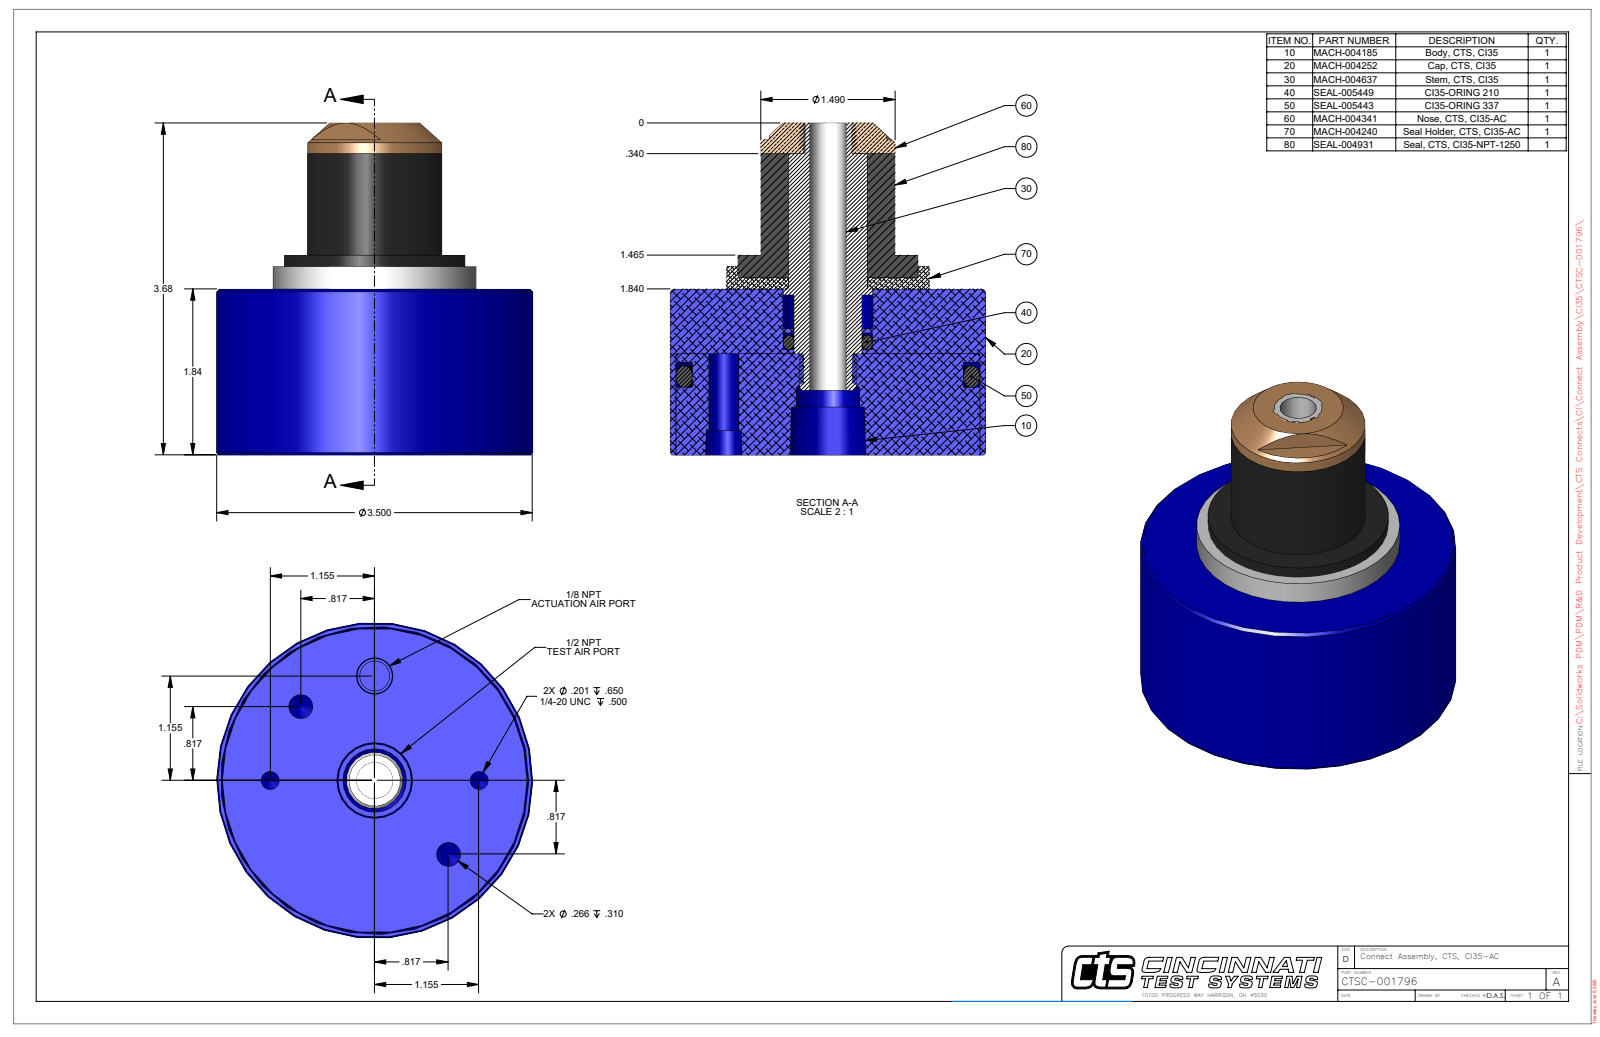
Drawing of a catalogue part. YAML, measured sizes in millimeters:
part_name: "CTSC-001796"
step_written_by: "SolidWorks 2023 (AUTOMOTIVE_DESIGN)"
units: millimeters
bodies: {solids: 1, faces: 66, planar: 19, cylindrical: 27, other: 20}
overall_size: [93.5, 88.9, 88.9]
volume: 337200
surface_area: 45490
round_holes:
  - {diameter: 5.1, count: 2}
  - {diameter: 6.8, count: 2}
  - {diameter: 8.4, count: 1}
  - {diameter: 10.3, count: 1}
  - {diameter: 17.9, count: 1}
  - {diameter: 85.7, count: 1}
round_bosses_or_shafts:
  - {diameter: 88.9, count: 1}
  - {diameter: 85.5, count: 1}
  - {diameter: 57.2, count: 1}
  - {diameter: 50.8, count: 1}
  - {diameter: 37.8, count: 1}
partial_cylinders:
  - {radius: 6.8, count: 1}
face_to_face_distances: [46.7, 56.3, 9.5, 53.1, 6.4, 3.2, 93.5, 46.7, 40.4, 37.2]
hole_center_spacings: [22.5, 29.3, 54.2, 29.3, 41.5, 58.6, 58.7]
